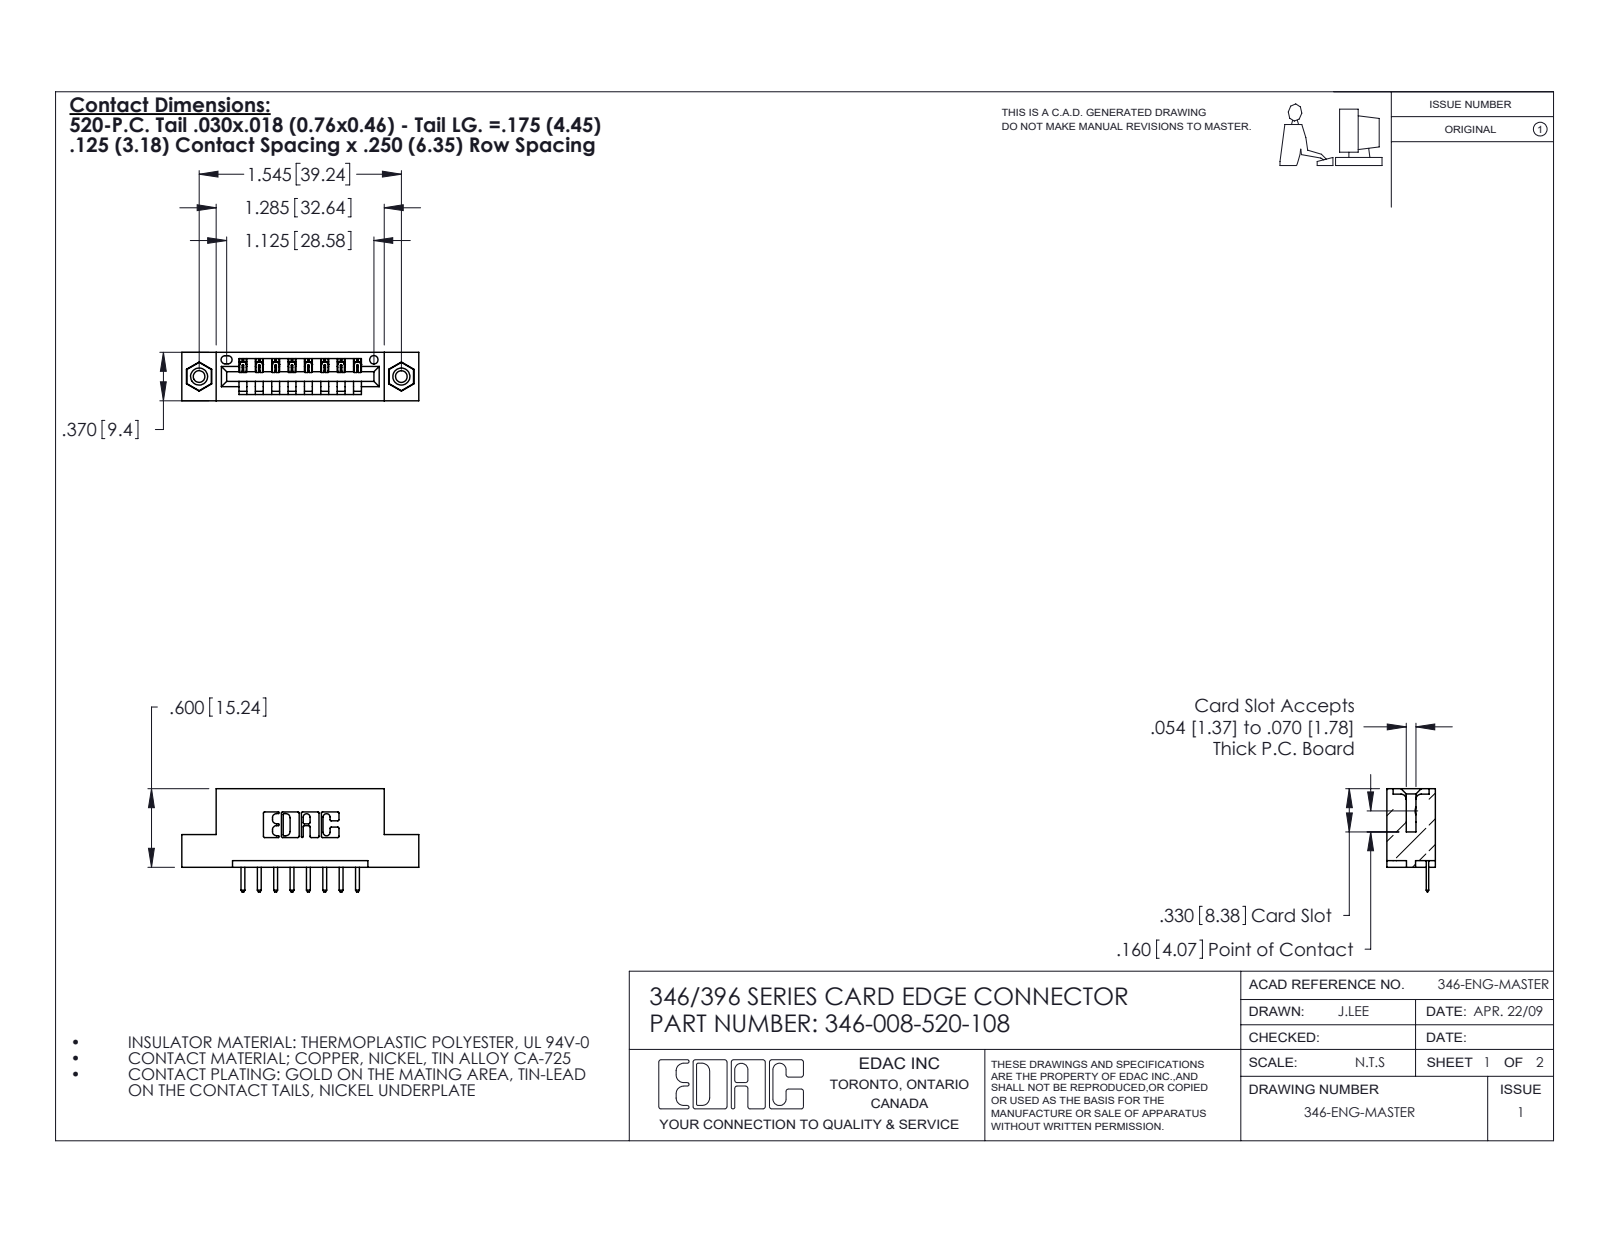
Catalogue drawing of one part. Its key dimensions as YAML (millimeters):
part_name: "345-250-001_345-250-003-102; 346 Part_Flush Mounting Lugs - 0.156 Dia-TI; 346-008-520-108; 345-292-001_345-293-120"
step_written_by: "SolidWorks 2020 (CONFIG_CONTROL_DESIGN)"
units: millimeters
bodies: {solids: 11, faces: 678, planar: 444, cylindrical: 218, other: 16}
overall_size: [46, 20, 9.4]
volume: 4130
surface_area: 4749
round_holes:
  - {diameter: 2.3, count: 2}
  - {diameter: 3.2, count: 2}
  - {diameter: 4, count: 2}
  - {diameter: 1.6, count: 1}
round_bosses_or_shafts:
  - {diameter: 3.9, count: 2}
partial_cylinders:
  - {radius: 0.3, count: 22}
  - {radius: 0.3, count: 18}
  - {radius: 0.2, count: 16}
  - {radius: 0.2, count: 6}
  - {radius: 0.8, count: 6}
  - {radius: 0.7, count: 3}
  - {radius: 0.8, count: 2}
  - {radius: 1, count: 2}
face_to_face_distances: [6.4, 9.4, 1.2, 8.2, 12.7, 3.8, 5.6, 2.5, 4.4, 3.2]
hole_center_spacings: [6.2, 34.1, 39.2]
